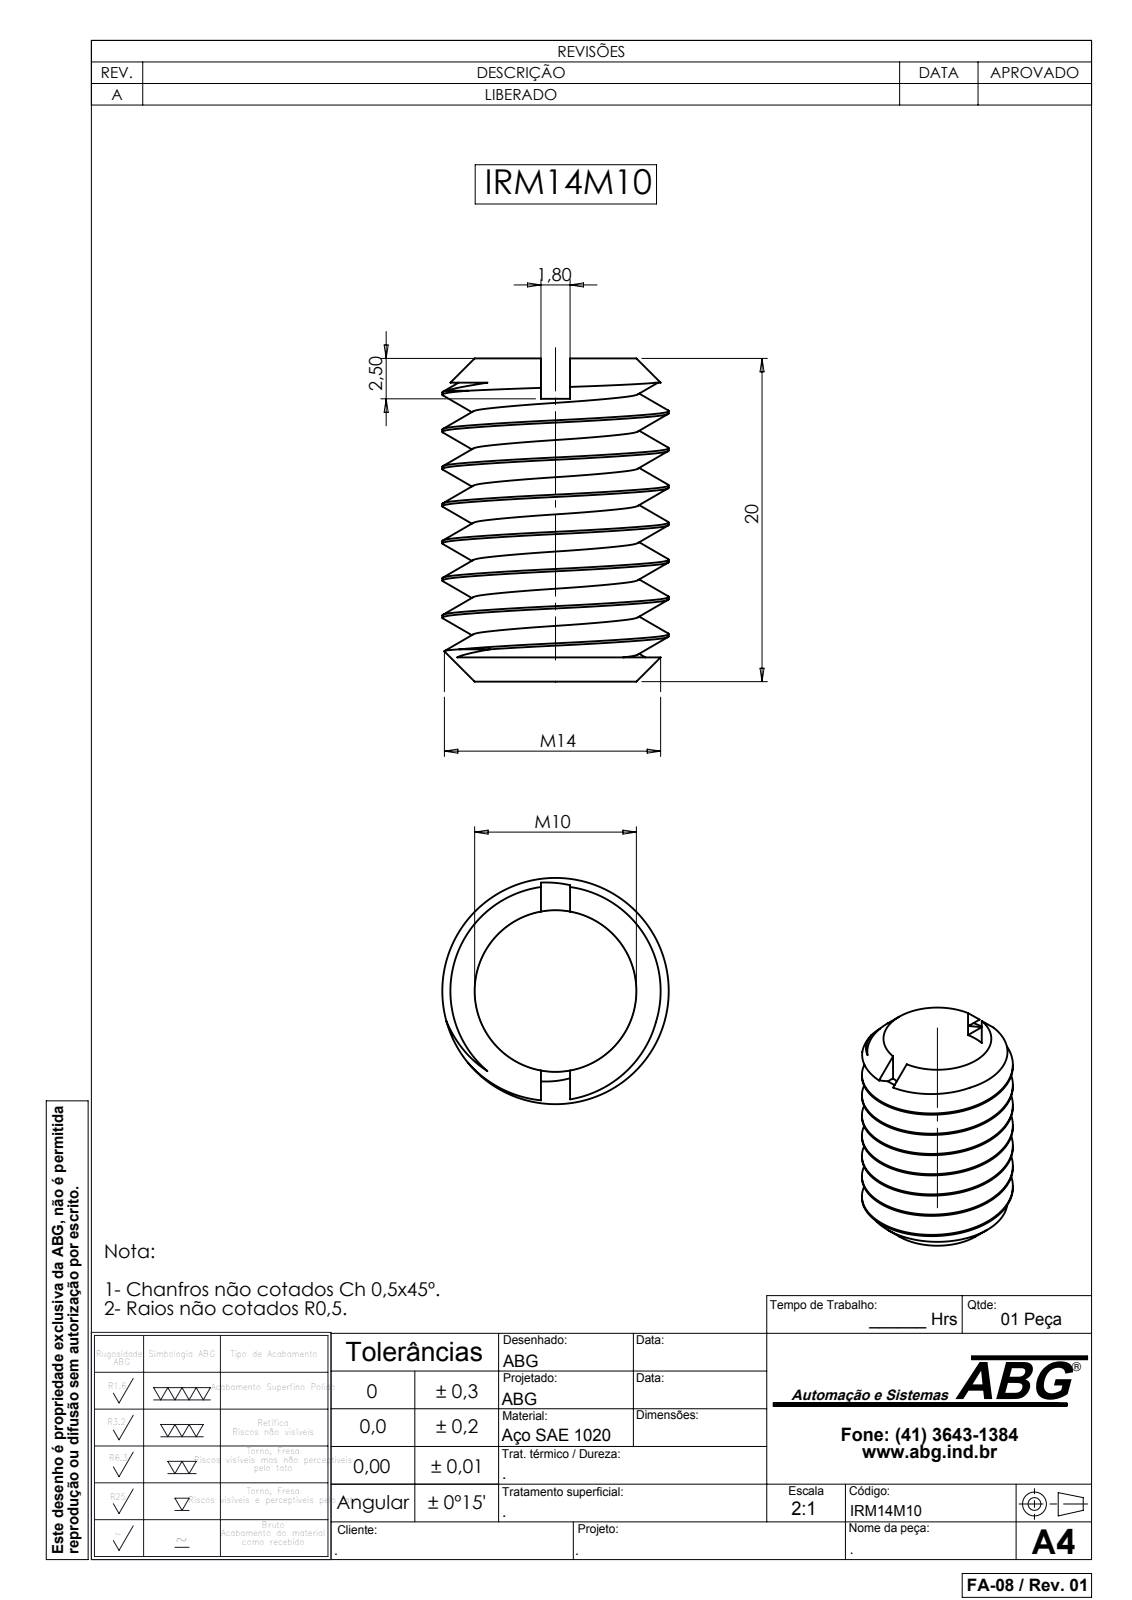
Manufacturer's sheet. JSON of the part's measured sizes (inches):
{"part_name": "IRM14M10", "step_written_by": "SolidWorks 2007 (CONFIG_CONTROL_DESIGN)", "units": "inches", "bodies": {"solids": 1, "faces": 33, "planar": 9, "cylindrical": 17, "other": 7}, "overall_size": [0.787, 0.551, 0.551], "volume_in3": 0.046, "surface_area_in2": 3.205, "round_holes": [[0.394, 1]], "round_bosses_or_shafts": [[0.551, 1]], "face_to_face_distances": [0.669, 0.071, 0.039, 0.63]}
